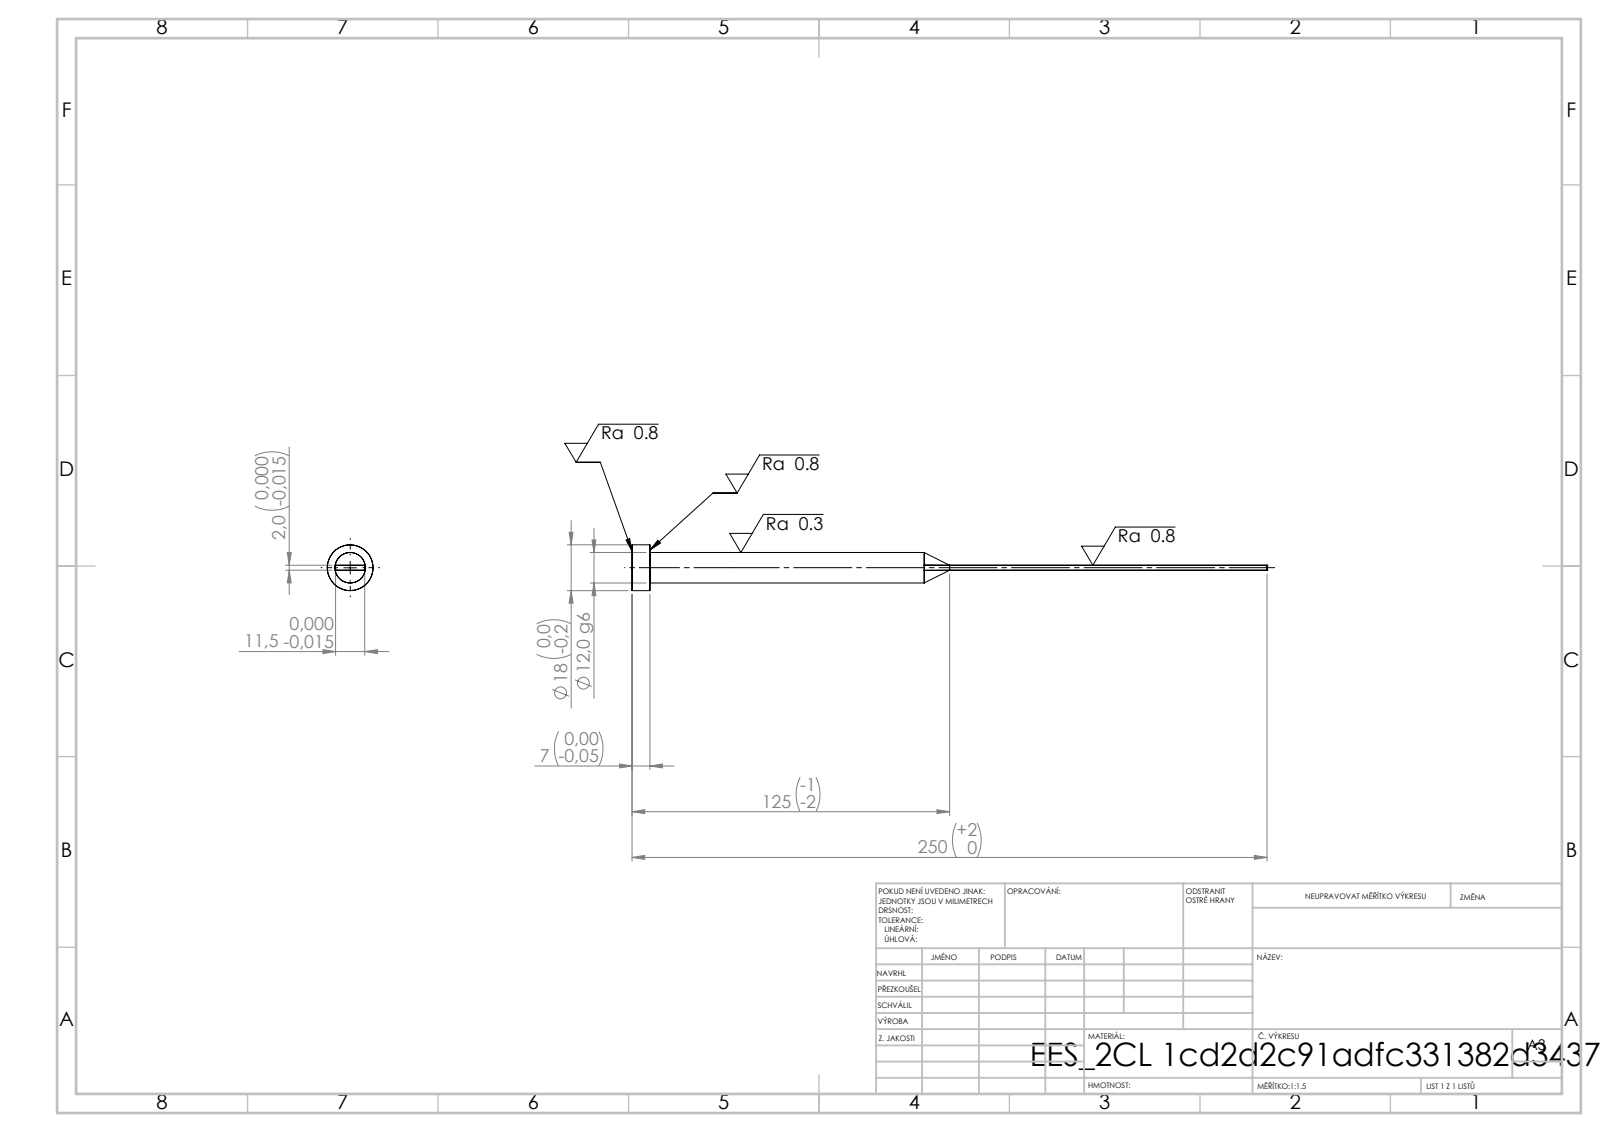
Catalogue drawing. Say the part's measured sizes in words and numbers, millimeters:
Its 3-D file was written by "SolidWorks 2019 (CONFIG_CONTROL_DESIGN)". It is 1 solid with 15 faces: 7 planar, 4 cylindrical and 4 other. Overall it measures 250 by 18 by 18 millimeters. Its volume is 17 517 cubic millimeters and its surface area 8 586 square millimeters. Round bosses or shafts: 1 of diameter 18, 1 of diameter 12. The main face-to-face distances are 2, 11.5, 7, 250, 243.
